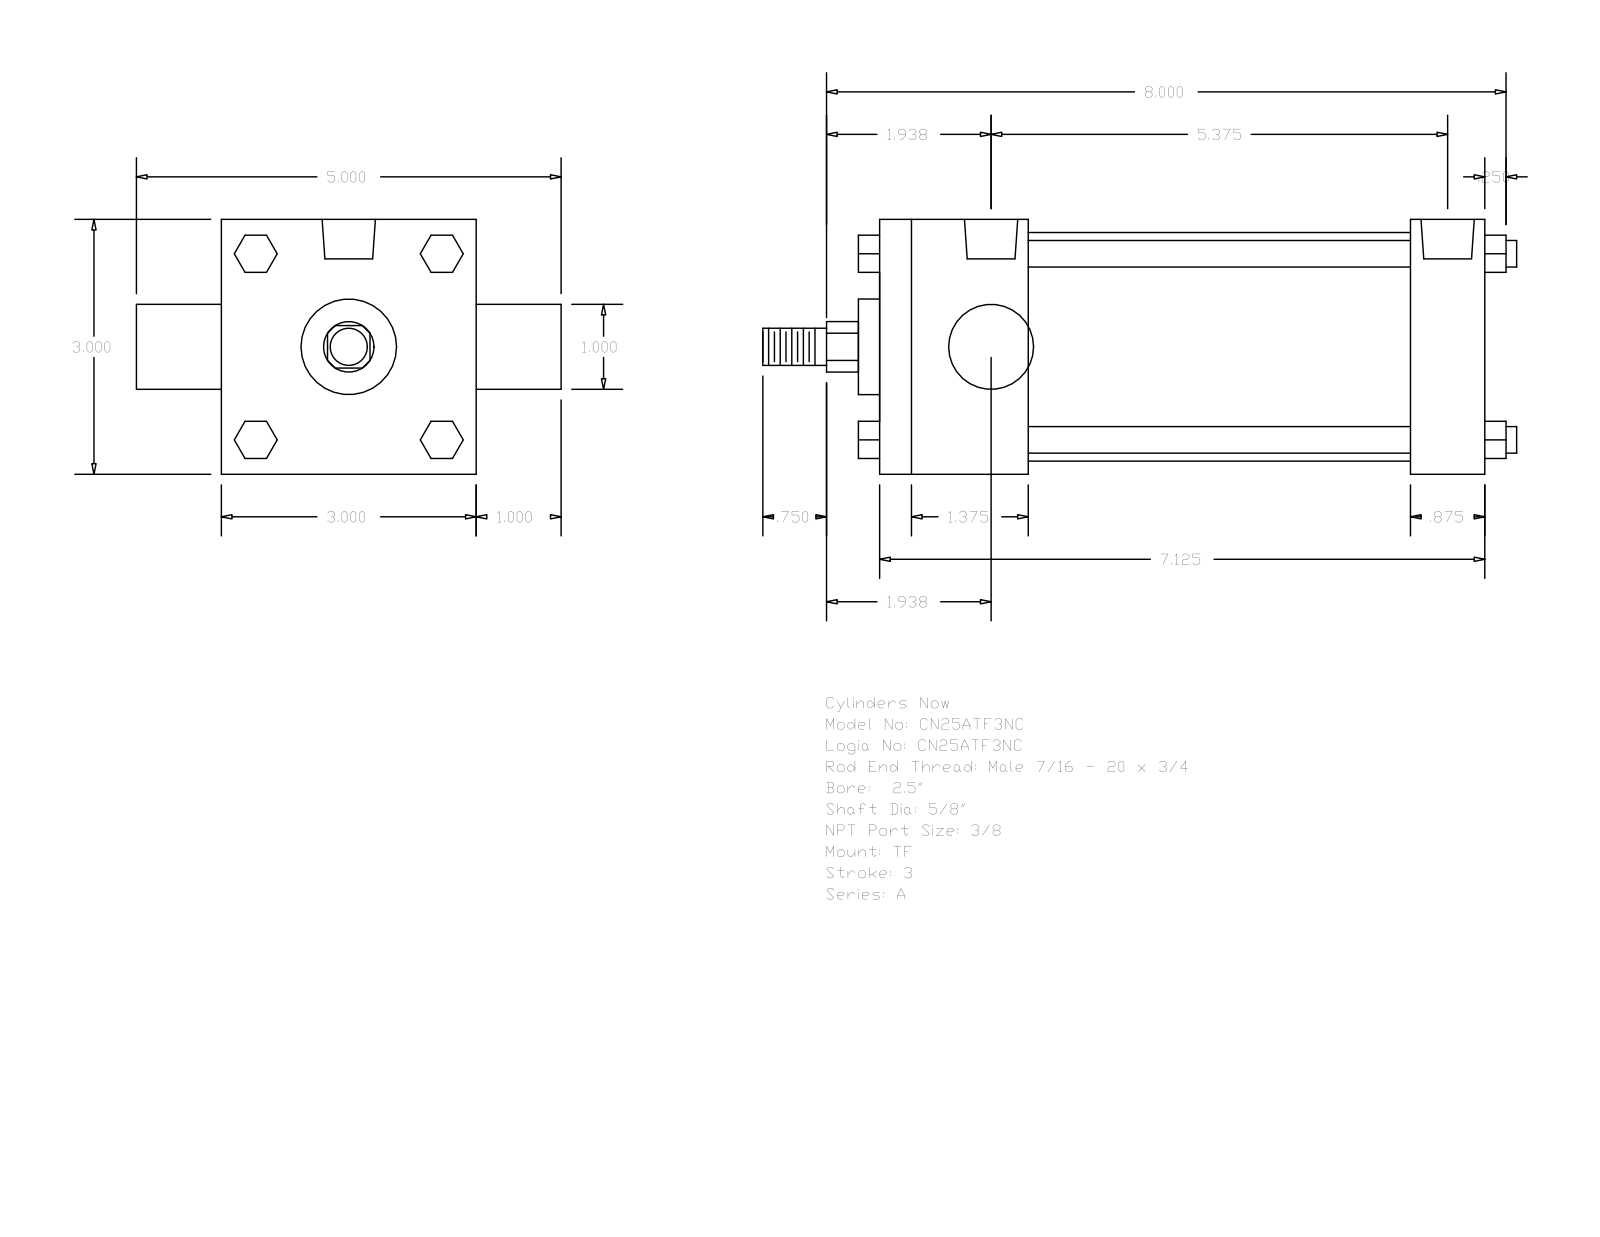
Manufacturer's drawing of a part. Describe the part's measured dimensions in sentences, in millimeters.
The part is named "A_TF__0250_0.625". Its 3-D file was written by "GSSL Pune (CONFIG_CONTROL_DESIGN)". It is 0 solids with 120 faces: 92 planar, 28 cylindrical and 0 other. Overall it measures 225.43 by 127 by 76.2 millimeters. Round holes: 3 of diameter 5.56, 2 of diameter 15.93. Round bosses or shafts: 4 of diameter 7.94, 1 of diameter 68.33, 1 of diameter 28.57, 1 of diameter 25.4, 1 of diameter 15.88, 1 of diameter 11.11. Partial cylindrical surfaces (rounded edges, fillets, slot ends): 1 of radius 7.54. The main face-to-face distances are 76.2, 180.97, 44.45, 158.74, 114.29, 136.52, 22.23, 25.4, 101.6, 6.35. The hole center spacings are 2.38, 138.91, 136.53, 141.29.
